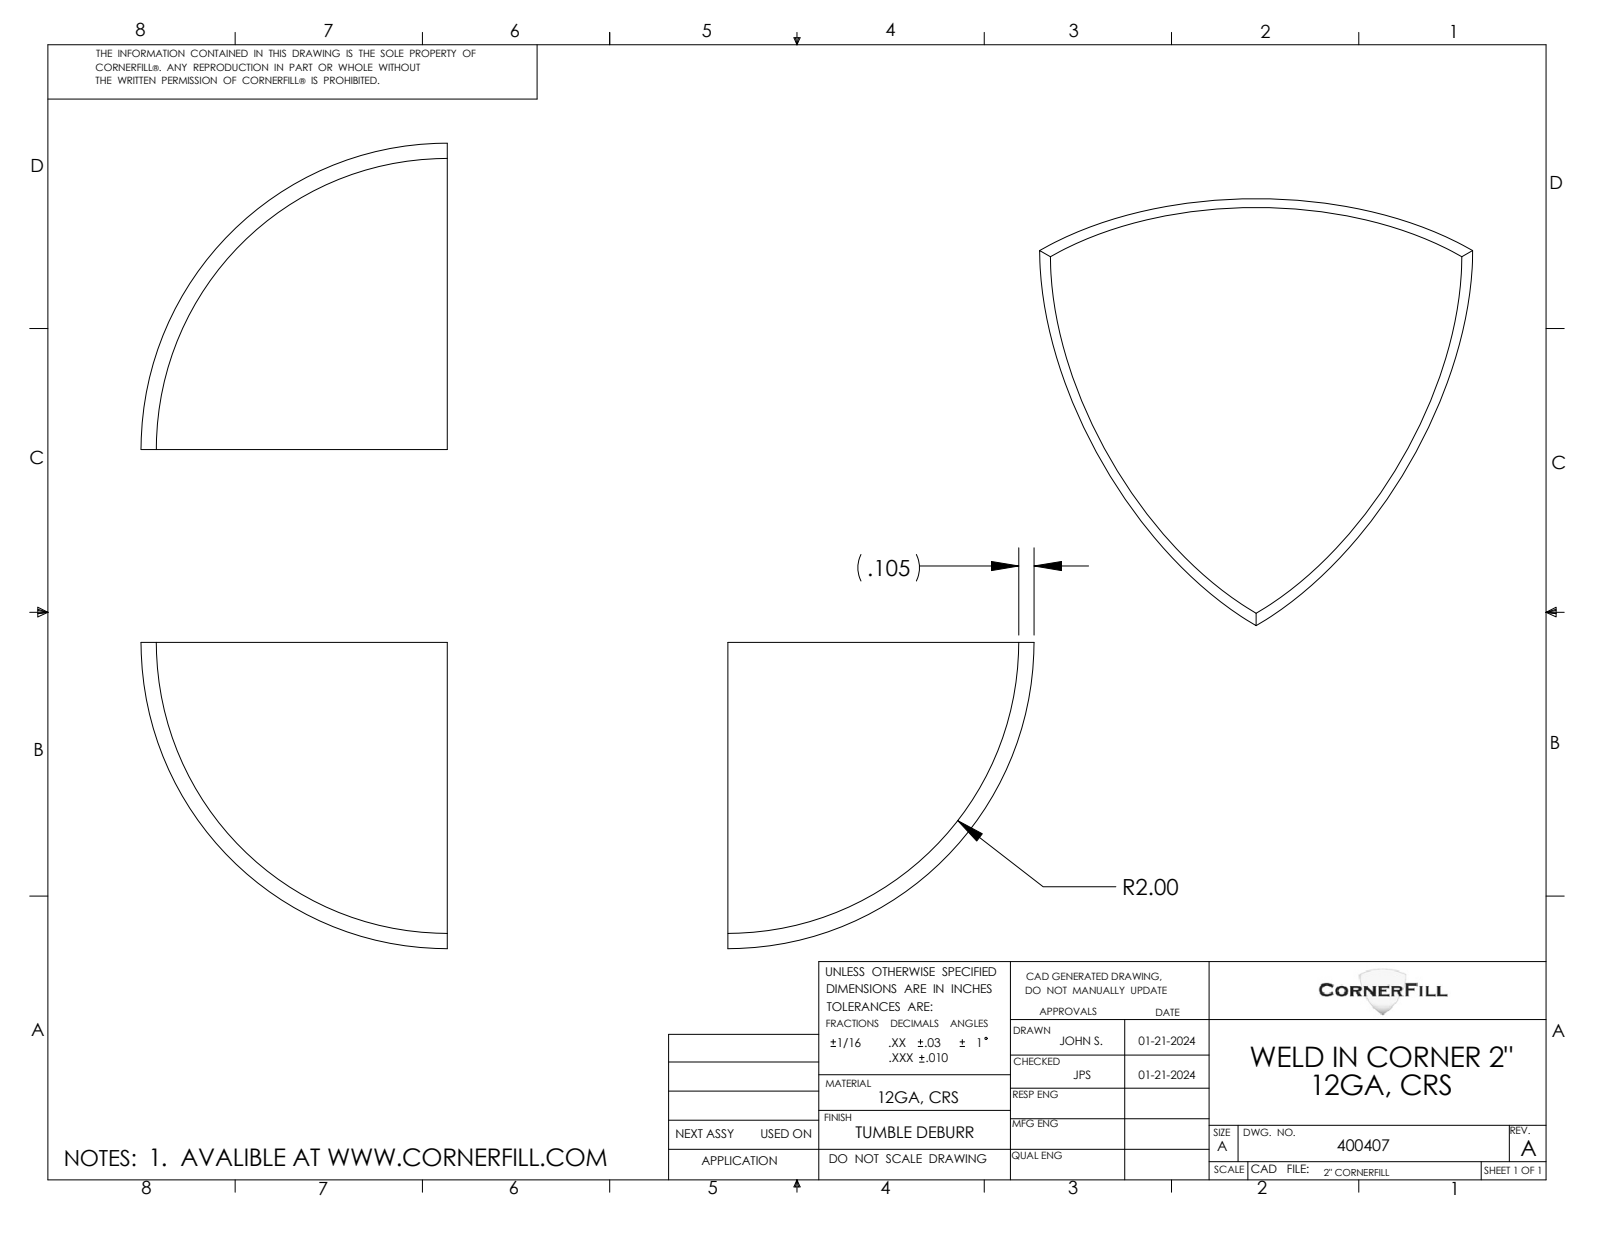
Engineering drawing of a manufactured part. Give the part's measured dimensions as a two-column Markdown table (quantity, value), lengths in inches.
| quantity | value |
| --- | --- |
| part name | 400407 |
| STEP written by | SolidWorks 2021 (CONFIG_CONTROL_DESIGN) |
| units | inches |
| bodies | 1 solid, 5 faces (3 planar, 0 cylindrical, 2 other) |
| overall size | 2.977 × 2.105 × 2.105 |
| volume | 0.695 in³ |
| surface area | 14.26 in² |
